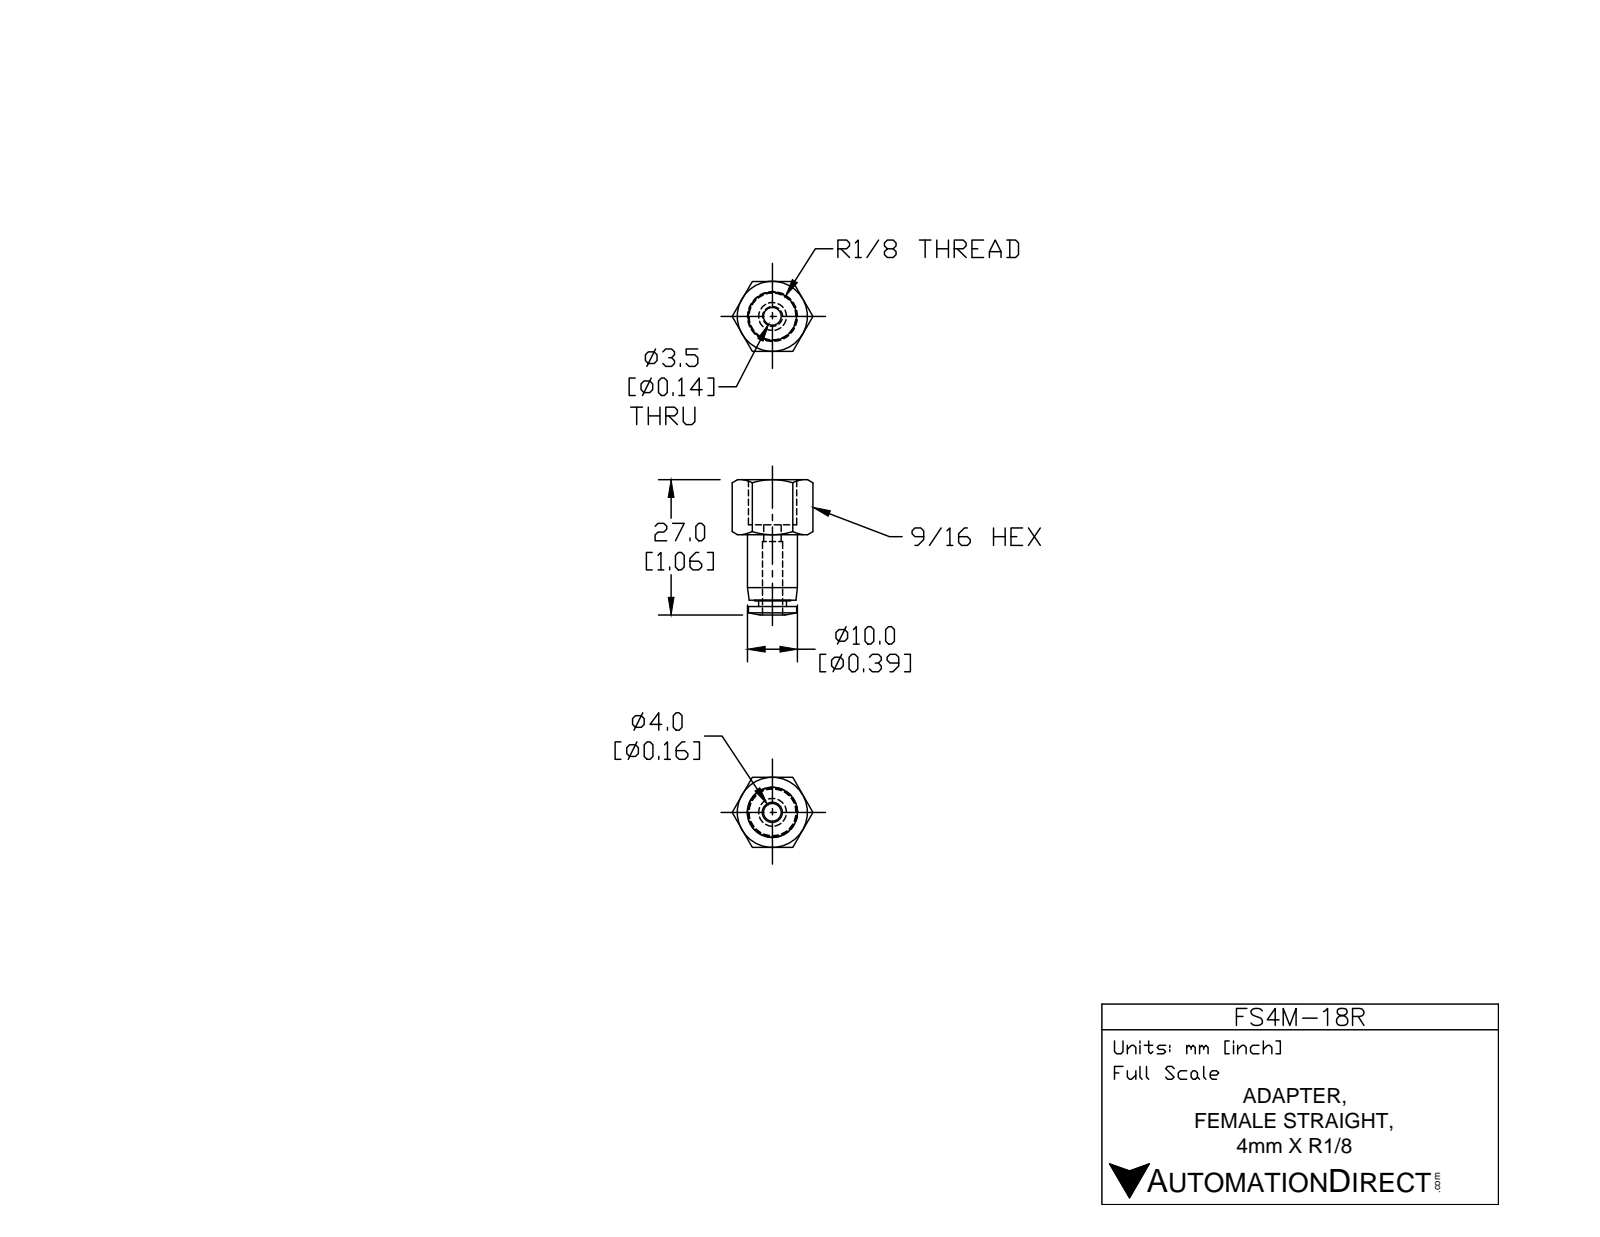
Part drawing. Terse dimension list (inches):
name: FS4M-18R
written by: SolidWorks 2015 (AUTOMOTIVE_DESIGN)
unit: in
bodies: 1 solid, 48 faces (14 planar, 12 cylindrical, 22 other)
size: 1.065 × 0.636 × 0.551
volume: 0.131 in³; area: 2.934 in²
holes: 1× ⌀0.138, 1× ⌀0.169
bosses: 1× ⌀0.394, 1× ⌀0.382, 1× ⌀0.283, 1× ⌀0.22
face distances: 0.551, 0.433, 0.354, 0.079, 0.998, 0.644, 0.565, 0.949, 0.594, 0.516
